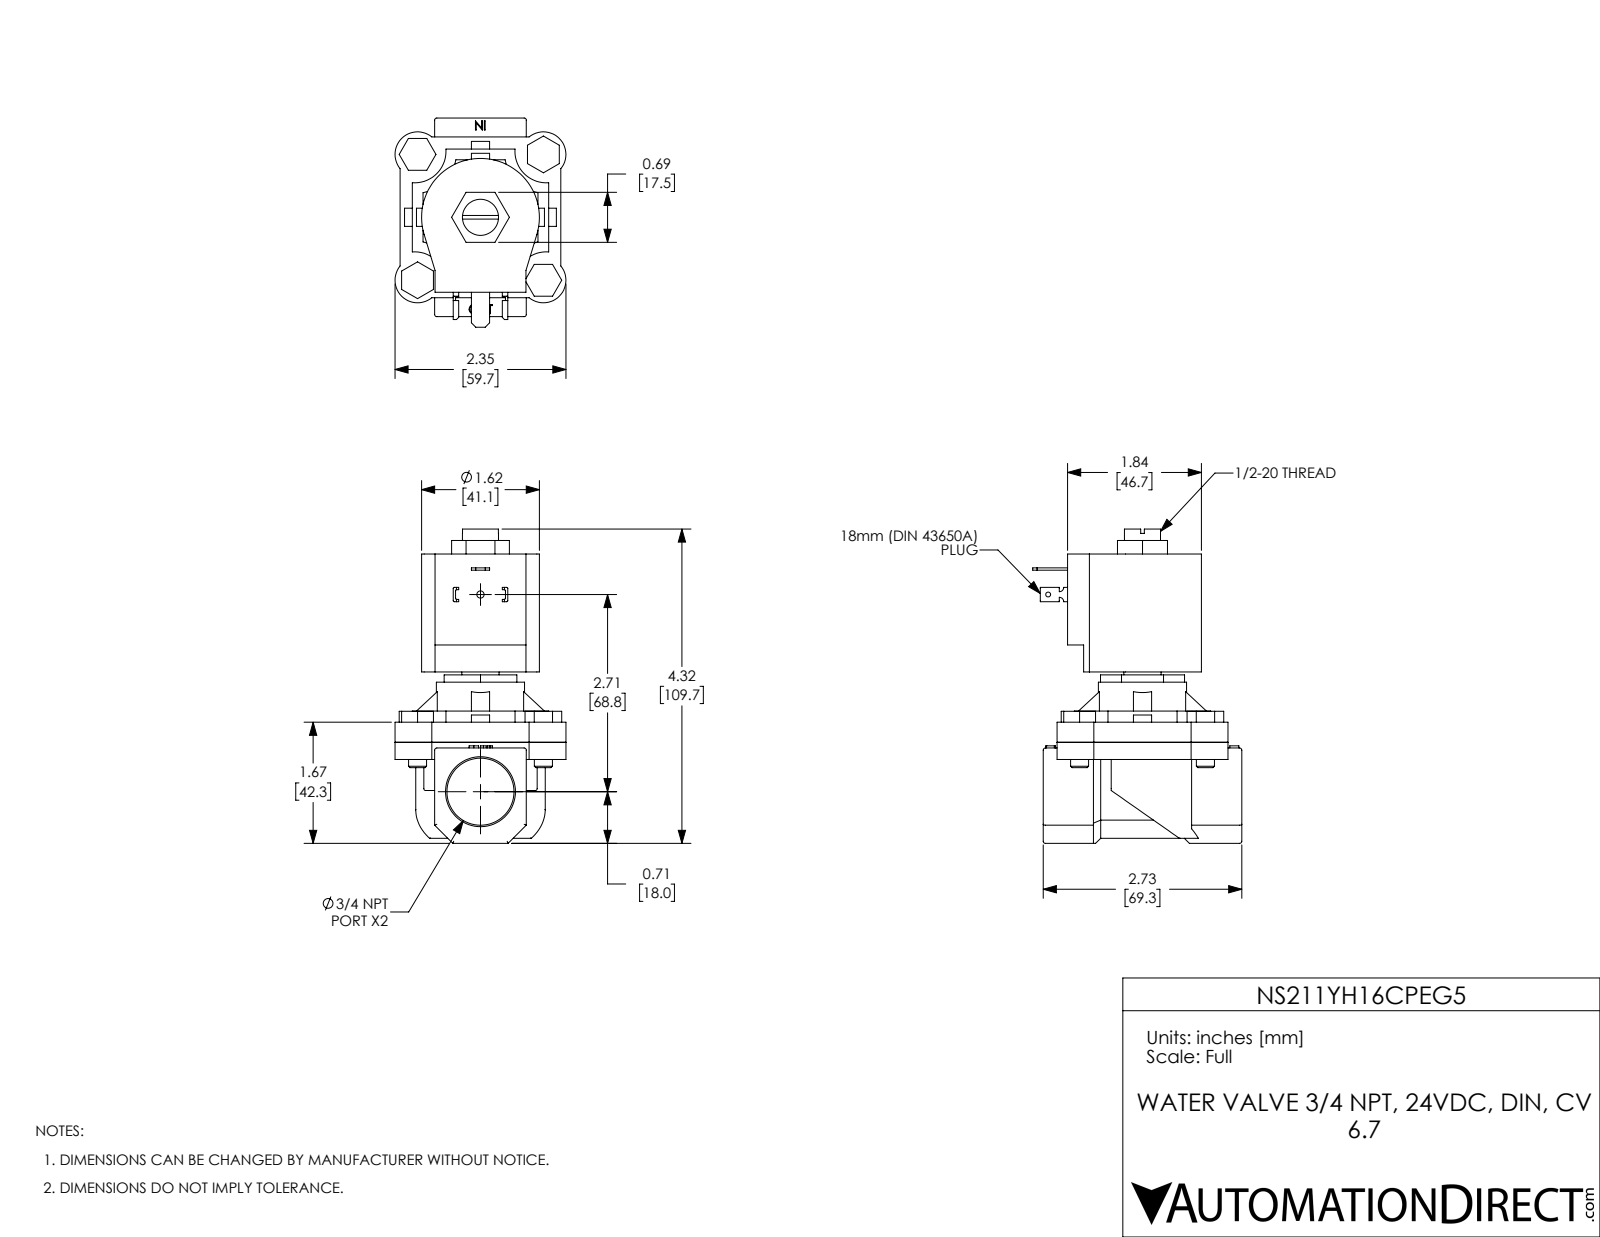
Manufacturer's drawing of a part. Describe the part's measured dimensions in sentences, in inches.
The part is named "NS211YH16CPEG5". Its 3-D file was written by "SolidWorks 2024 (CONFIG_CONTROL_DESIGN)". It is 11 solids with 387 faces: 241 planar, 113 cylindrical and 33 other. Overall it measures 4.32 by 2.875 by 2.35 inches. Its volume is 10.62 cubic inches and its surface area 70.92 square inches. Round holes: 4 of diameter 0.25, 1 of diameter 0.067, 1 of diameter 0.1, 1 of diameter 0.496, 1 of diameter 0.512, 1 of diameter 0.922, 1 of diameter 1.155. Round bosses or shafts: 4 of diameter 0.248, 1 of diameter 1.213. Partial cylindrical surfaces (rounded edges, fillets, slot ends): 15 of radius 0.03, 8 of radius 0.015, 4 of radius 0.31, 4 of radius 0.432, 4 of radius 0.579, 2 of radius 0.06, 1 of radius 0.81, 1 of radius 0.89. The main face-to-face distances are 0.276, 2.587, 2.311, 0.236, 0.512, 2.823, 0.475, 1.735, 1.26, 2.21. The hole center spacings are 1.223, 1.73, 2.446, 2.71.
